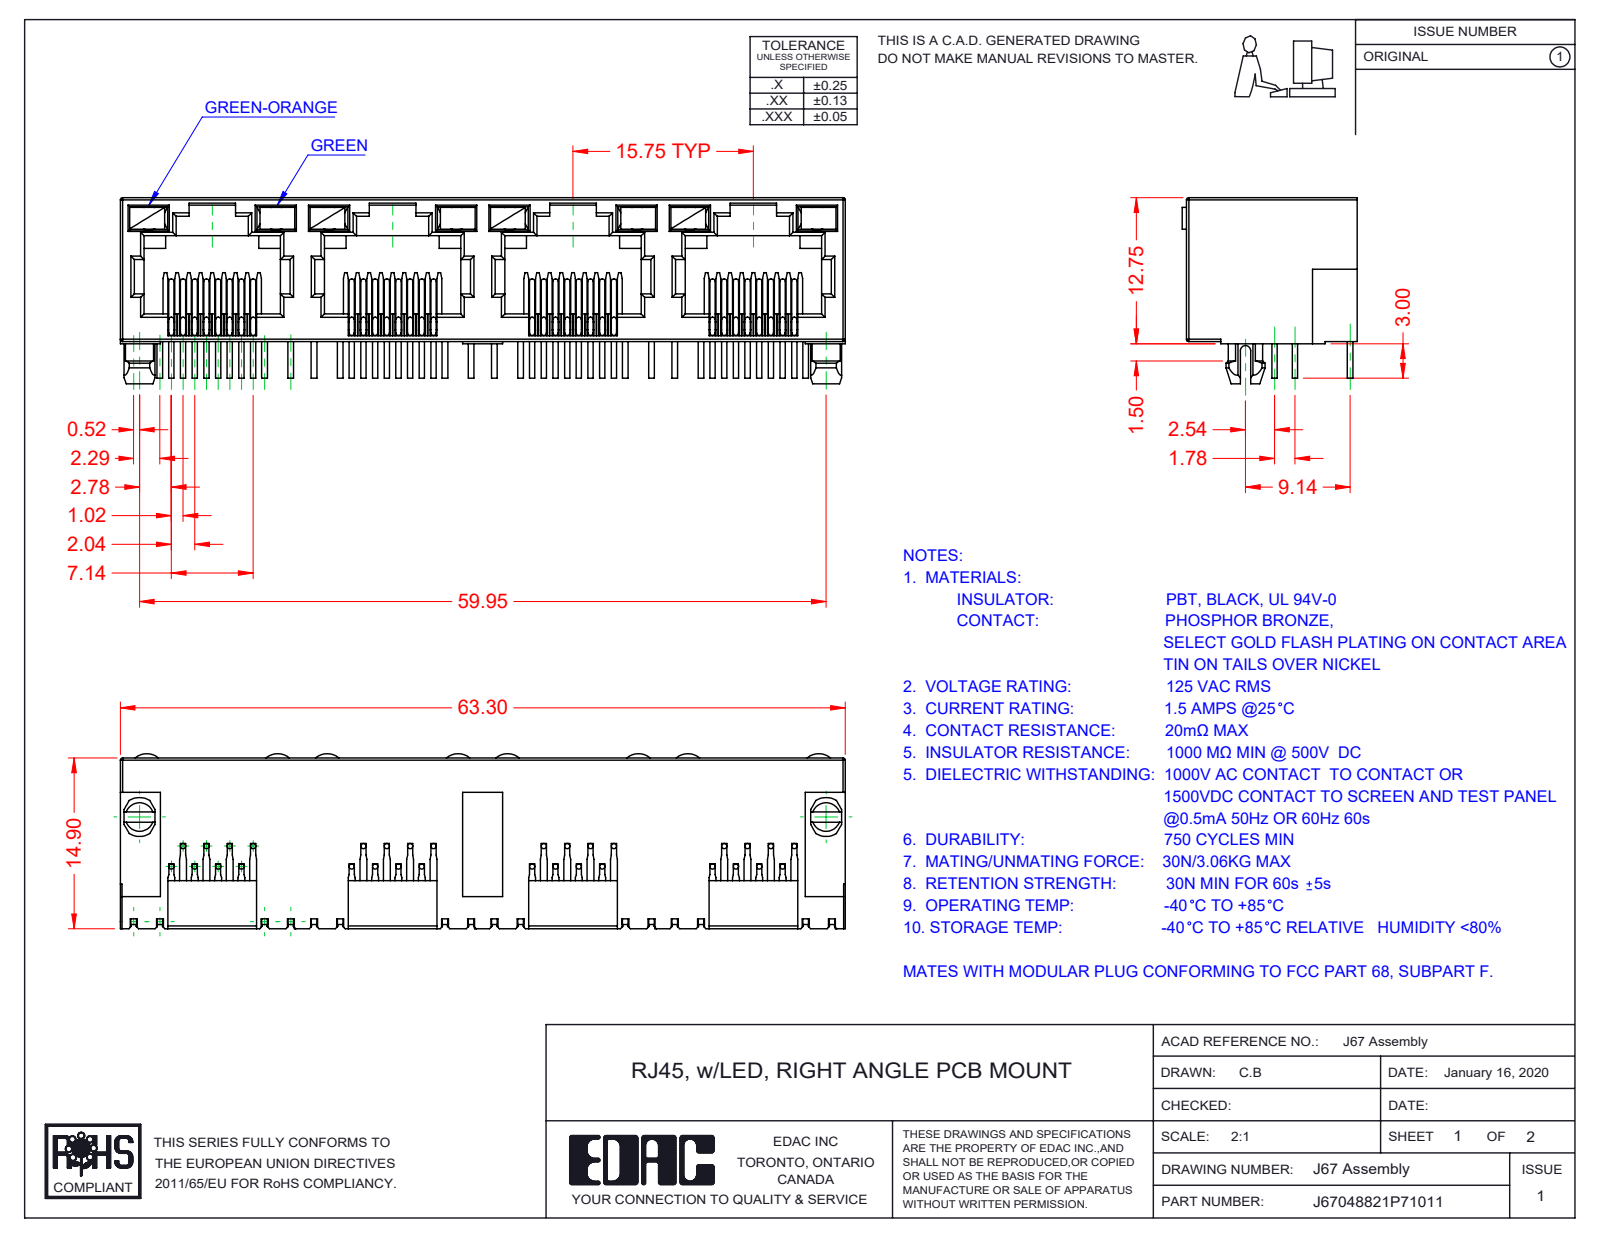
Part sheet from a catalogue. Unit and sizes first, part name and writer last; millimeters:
Units: millimetres
Overall size (bounding box): 63.3 × 16.25 × 15.28
Round bosses / shafts (diameter × count): ⌀0.46 ×96
Partial cylindrical surfaces — rounded edges, fillets, slot ends (radius × count): R0.2 ×66, R0.3 ×29, R0.45 ×9, R1.55 ×8, R1.5 ×2, R1.7 ×2, R0.35 ×1, R1 ×1
Main face-to-face distances: 0.5, 12.55, 1.89, 0.89, 10, 15.75, 1, 1.39, 11, 11.89
Volume: 5 159 mm³ · Surface area: 11 573 mm²
Bodies: 41 solids, 2473 faces (1781 planar, 484 cylindrical, 208 other)
Part name (STEP PRODUCT): 67 Contacts; 67 LED LH_7-Green-Orange; J67048822P73011; 67 LED RH_3-Green (+1 more)
STEP written by: SolidWorks 2016 (CONFIG_CONTROL_DESIGN)
